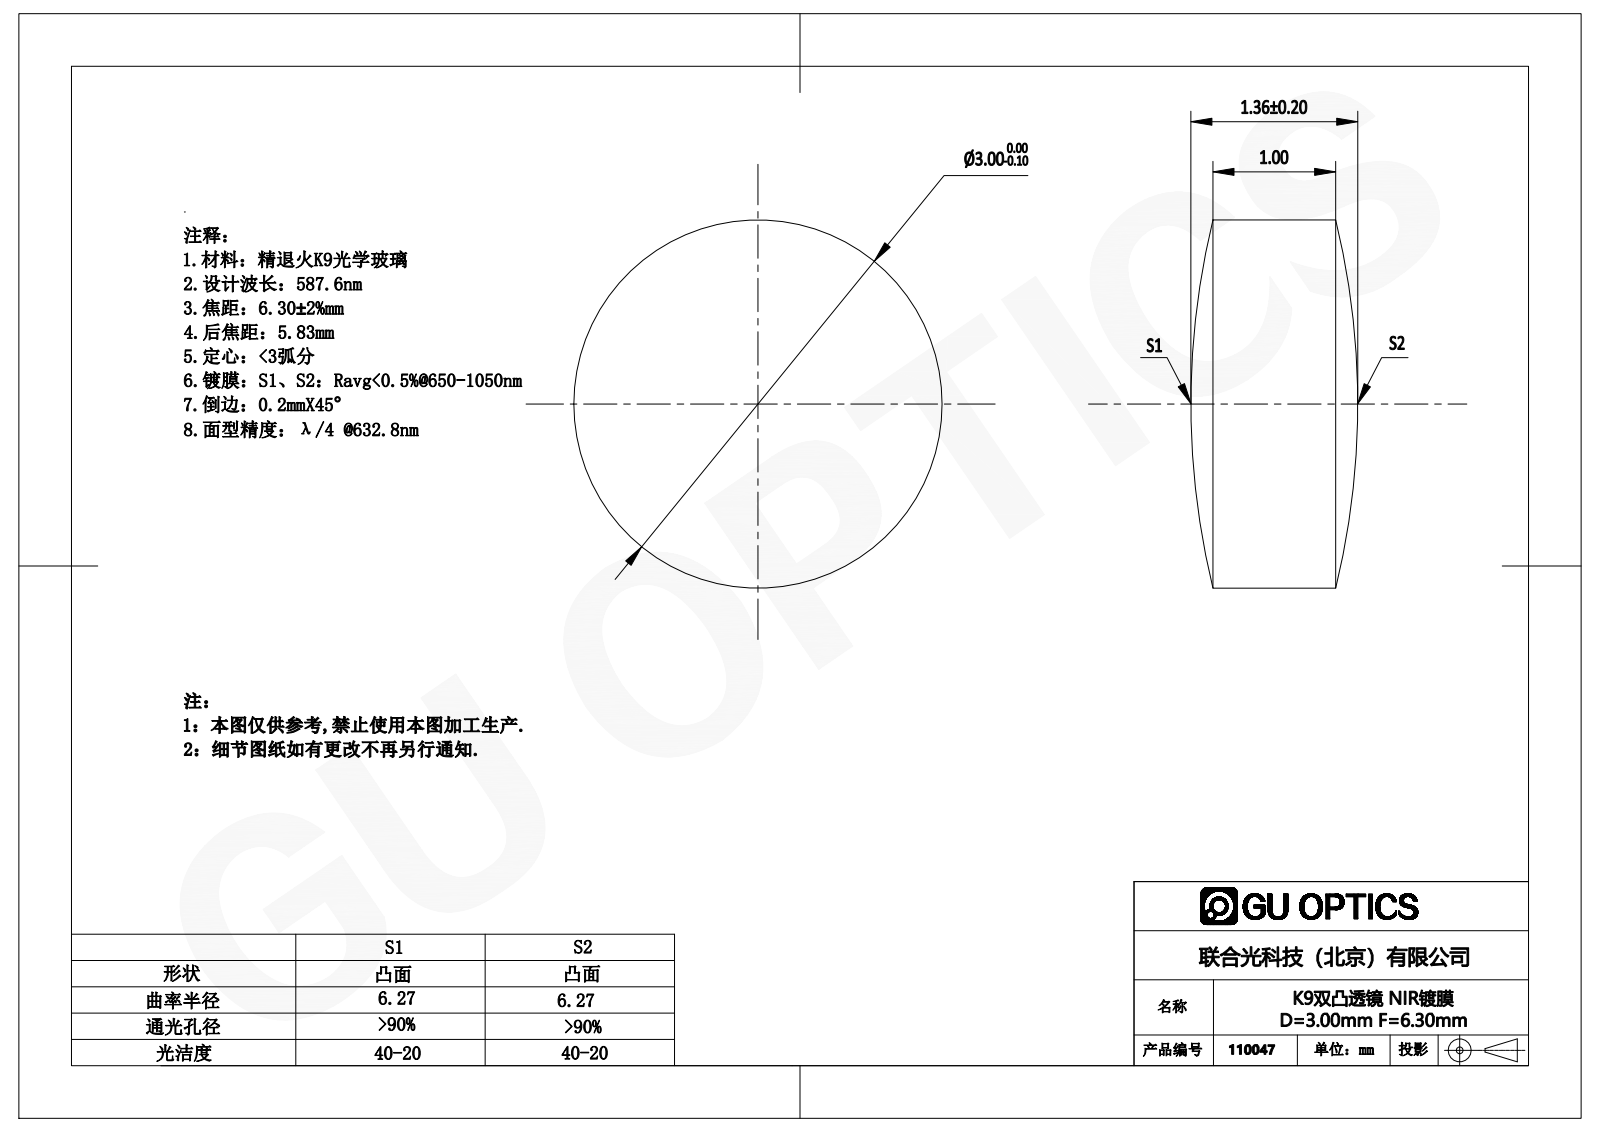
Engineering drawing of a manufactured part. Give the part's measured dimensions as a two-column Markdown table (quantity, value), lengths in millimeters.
| quantity | value |
| --- | --- |
| part name | 110003 |
| STEP written by | SolidWorks 2016 (CONFIG_CONTROL_DESIGN) |
| units | millimeters |
| bodies | 1 solid, 6 faces (0 planar, 2 cylindrical, 4 other) |
| overall size | 3 × 3 × 1.36 |
| volume | 8 mm³ |
| surface area | 24 mm² |
| round bosses / shafts (diameter × count) | 3 × 1 |
